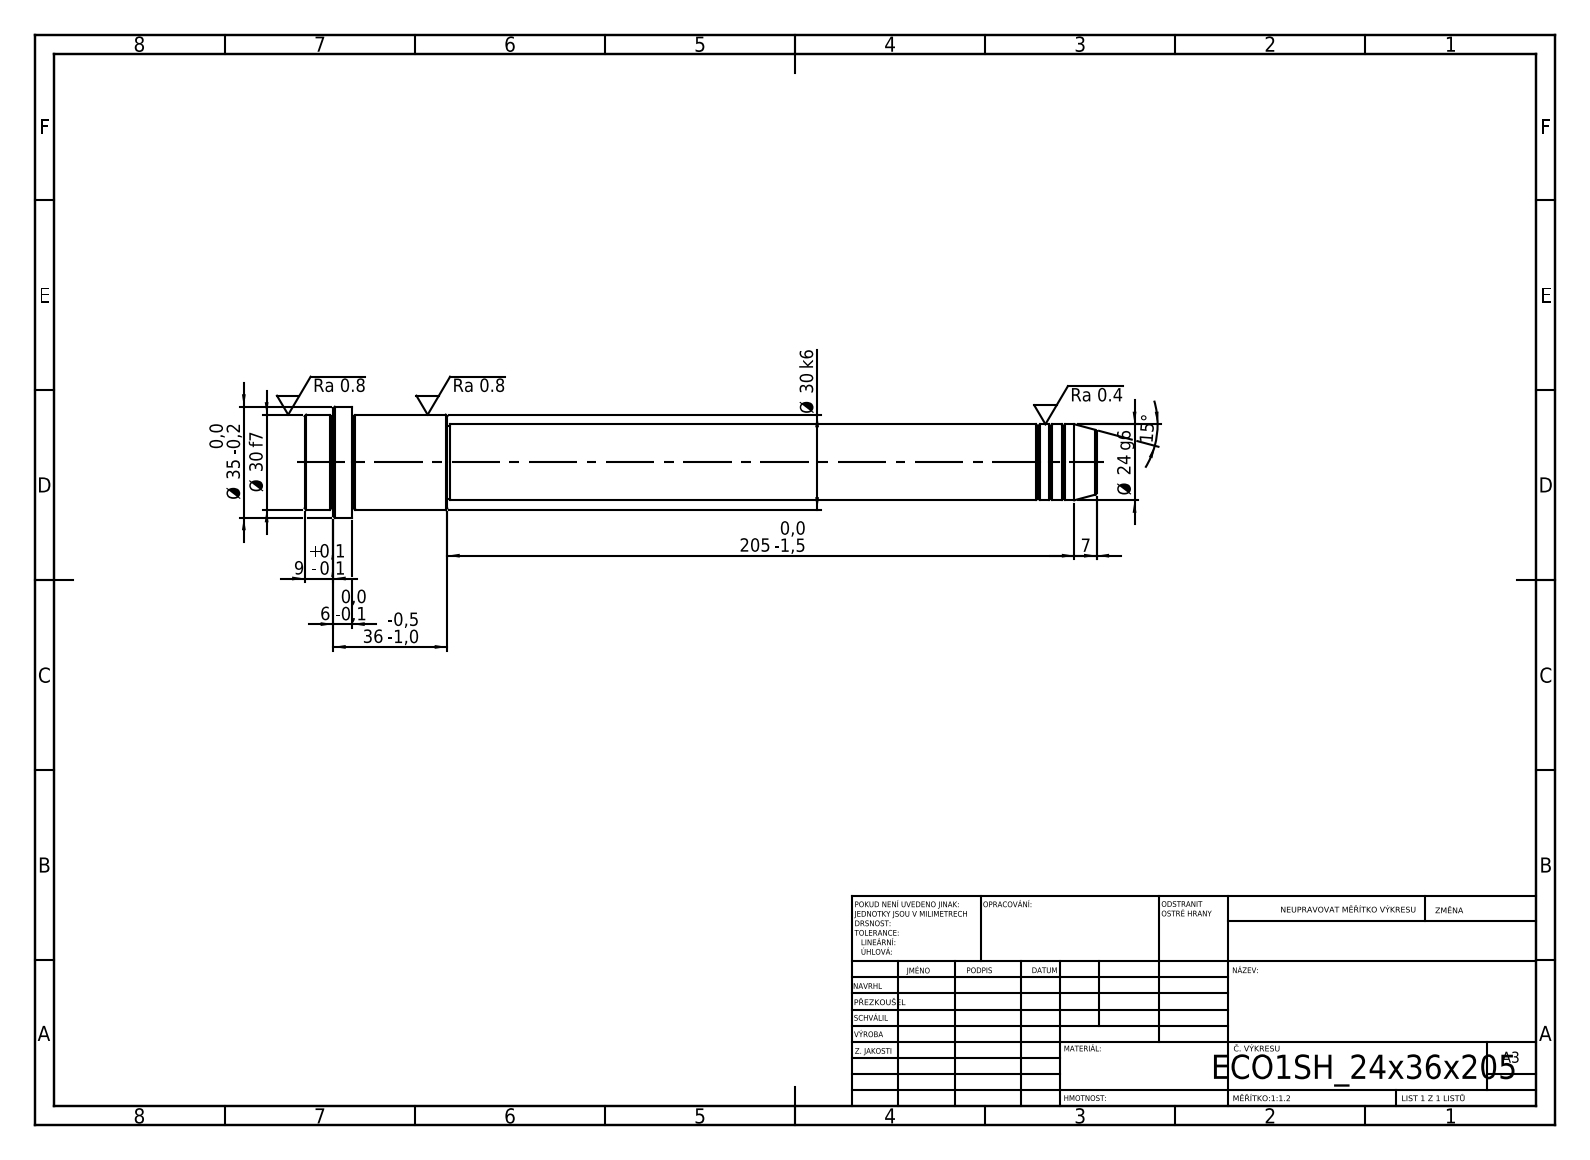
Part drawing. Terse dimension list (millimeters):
written by: SolidWorks 2019 (CONFIG_CONTROL_DESIGN)
unit: mm
bodies: 1 solid, 52 faces (6 planar, 16 cylindrical, 30 other)
size: 250 × 35 × 35
volume: 125 375 mm³; area: 21 758 mm²
bosses: 1× ⌀35, 1× ⌀30, 1× ⌀24, 1× ⌀23
face distances: 250, 235, 15, 205, 30, 45, 241, 36, 6, 9
